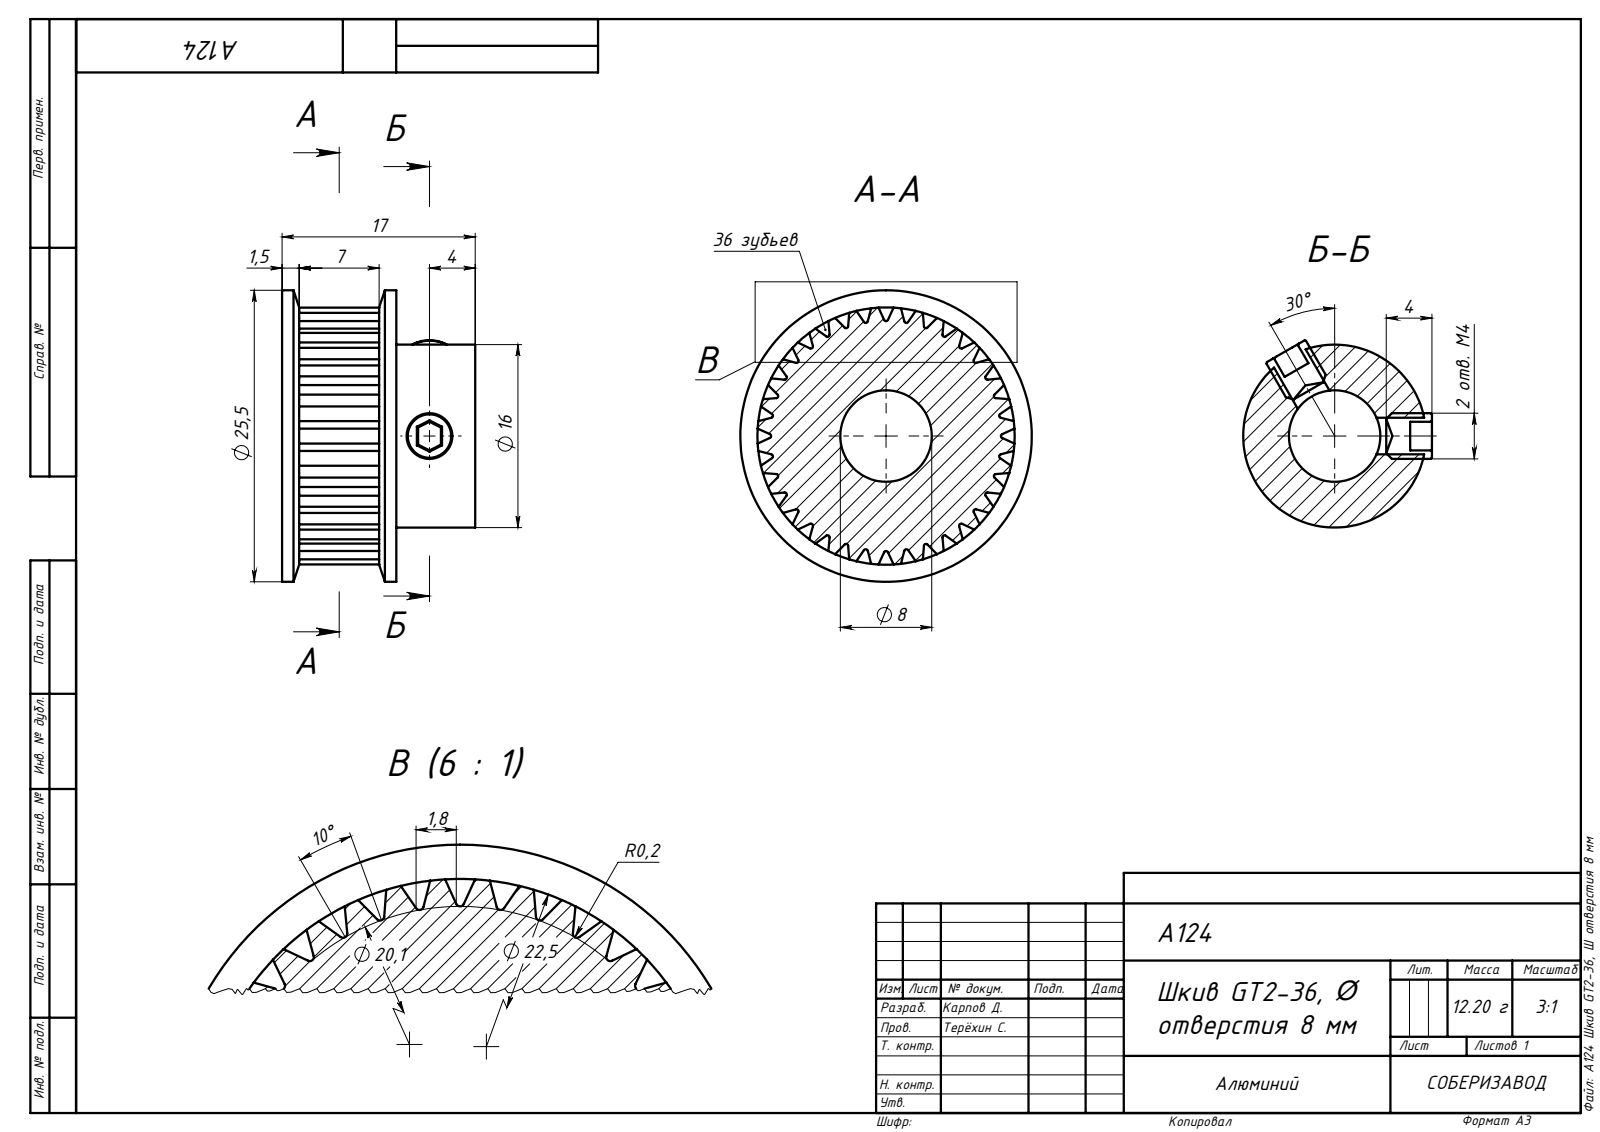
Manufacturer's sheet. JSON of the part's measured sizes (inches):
{"part_name": "41-1 (2); A124 Шкив GT2-36, O отверстия 8 мм", "step_written_by": "SolidWorks 2019 (AUTOMOTIVE_DESIGN)", "units": "inches", "bodies": {"solids": 3, "faces": 295, "planar": 176, "cylindrical": 103, "other": 16}, "overall_size": [1.004, 1.004, 0.669], "volume_in3": 0.281, "surface_area_in2": 5.036, "round_holes": [[0.126, 2], [0.315, 1]], "round_bosses_or_shafts": [[0.157, 2], [1.004, 1], [0.709, 1], [0.63, 1]], "partial_cylinders_radius": [[0.007, 36], [0.443, 1]], "face_to_face_distances": [0.394, 0.32, 0.398, 0.272, 0.665, 0.669, 0.059, 0.335, 0.32, 0.606]}
